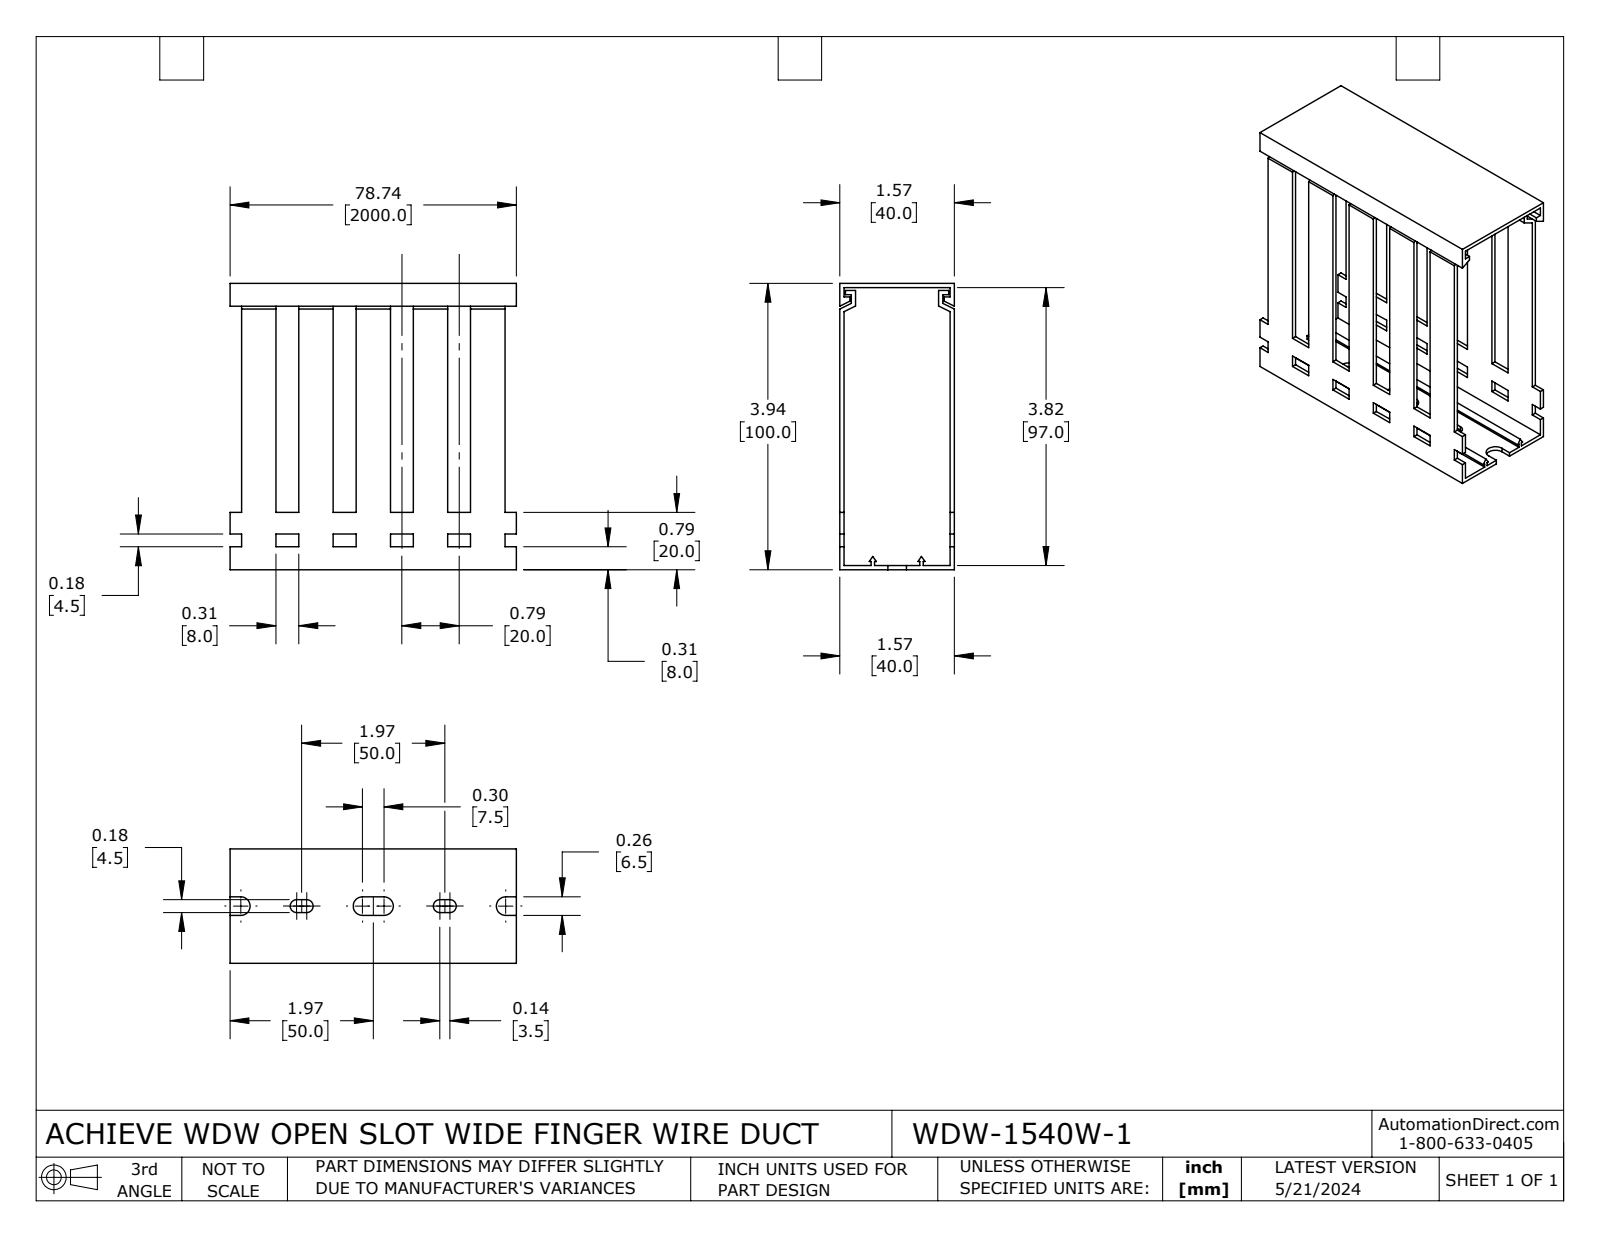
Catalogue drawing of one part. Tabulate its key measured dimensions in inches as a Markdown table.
| quantity | value |
| --- | --- |
| part name | WDW-1540W-1 |
| STEP written by | SolidWorks 2023 (CONFIG_CONTROL_DESIGN) |
| units | inches |
| bodies | 2 solids, 210 faces (198 planar, 12 cylindrical, 0 other) |
| overall size | 3.937 × 3.937 × 1.575 |
| volume | 2.126 in³ |
| surface area | 78.18 in² |
| partial cylindrical surfaces (radius × count) | 0.089 × 4, 0.128 × 4 |
| main face-to-face distances | 0.059, 1.516, 1.575, 3.878, 1.457, 3.937, 3.819, 0.787, 0.157, 0.472 |
